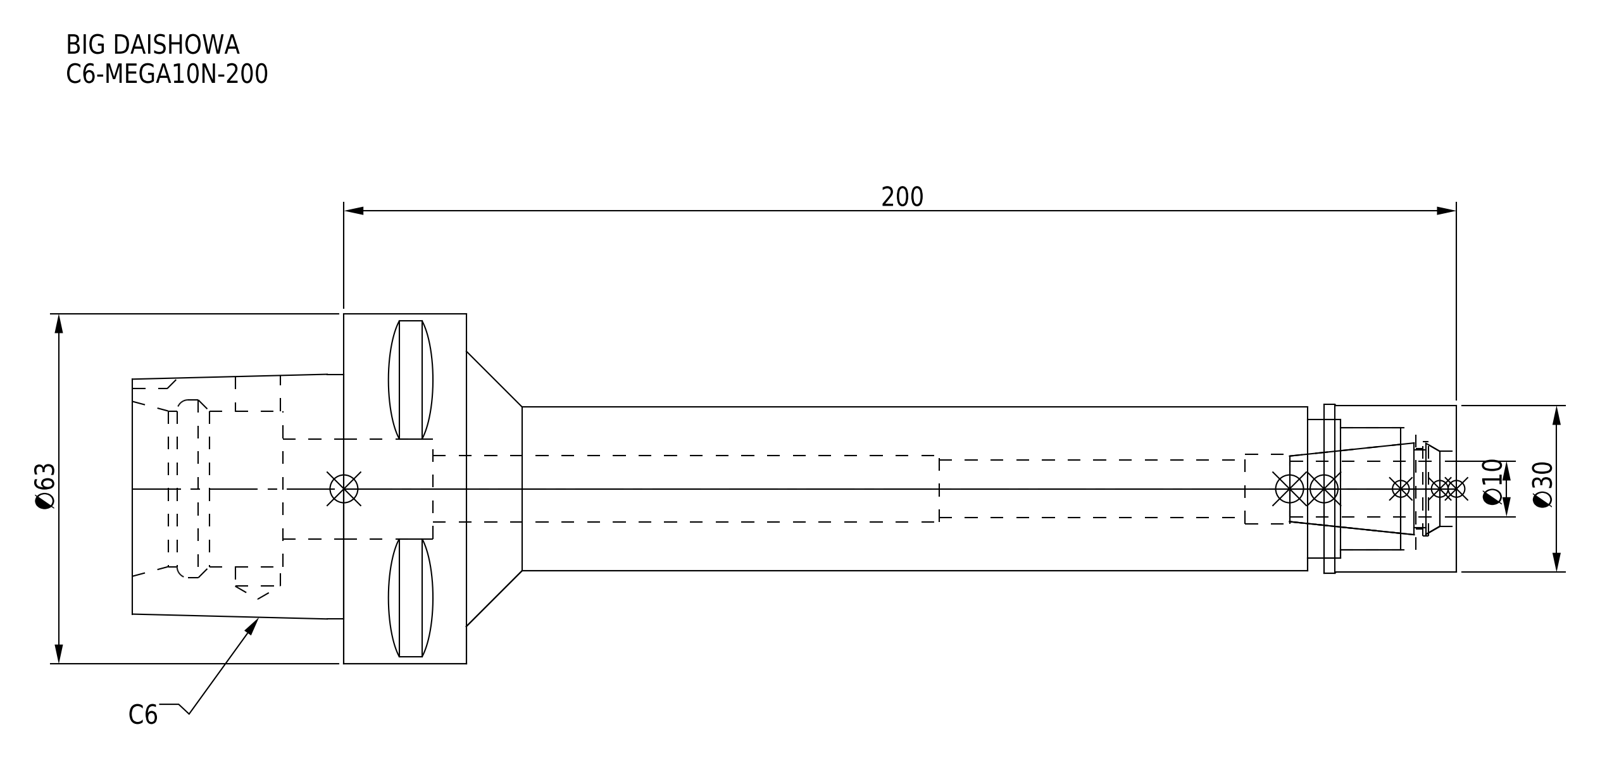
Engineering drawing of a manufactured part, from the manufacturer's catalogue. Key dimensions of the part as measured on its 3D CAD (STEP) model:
Part name (STEP PRODUCT): C6-MEGA10N-200-100_ASM.stp; C6-MEGA10N-200-100.stp; DXF_TEMP_ASSY_ASM_4_ASM.stp; C6-MEGA10N-200 (+3 more)
STEP written by: SolidWorks 2019 (CONFIG_CONTROL_DESIGN)
Units: millimetres
Bodies: 2 solids, 98 faces (39 planar, 41 cylindrical, 18 other)
Overall size (bounding box): 238 × 63 × 63
Volume: 202 681 mm³ · Surface area: 46 124 mm²
Round holes (diameter × count): ⌀8.1 ×1, ⌀10.4 ×1, ⌀12 ×1, ⌀12.5 ×1, ⌀13.5 ×1, ⌀14.5 ×1, ⌀17 ×1, ⌀18 ×1, ⌀22 ×1, ⌀25 ×1, ⌀28 ×1, ⌀32 ×1
Round bosses / shafts (diameter × count): ⌀63 ×1, ⌀30.3 ×1, ⌀30 ×1, ⌀29.5 ×1
Partial cylindrical surfaces — rounded edges, fillets, slot ends (radius × count): R5 ×1
Main face-to-face distances: 22, 178, 200, 38, 27, 238, 60, 33, 211, 11
